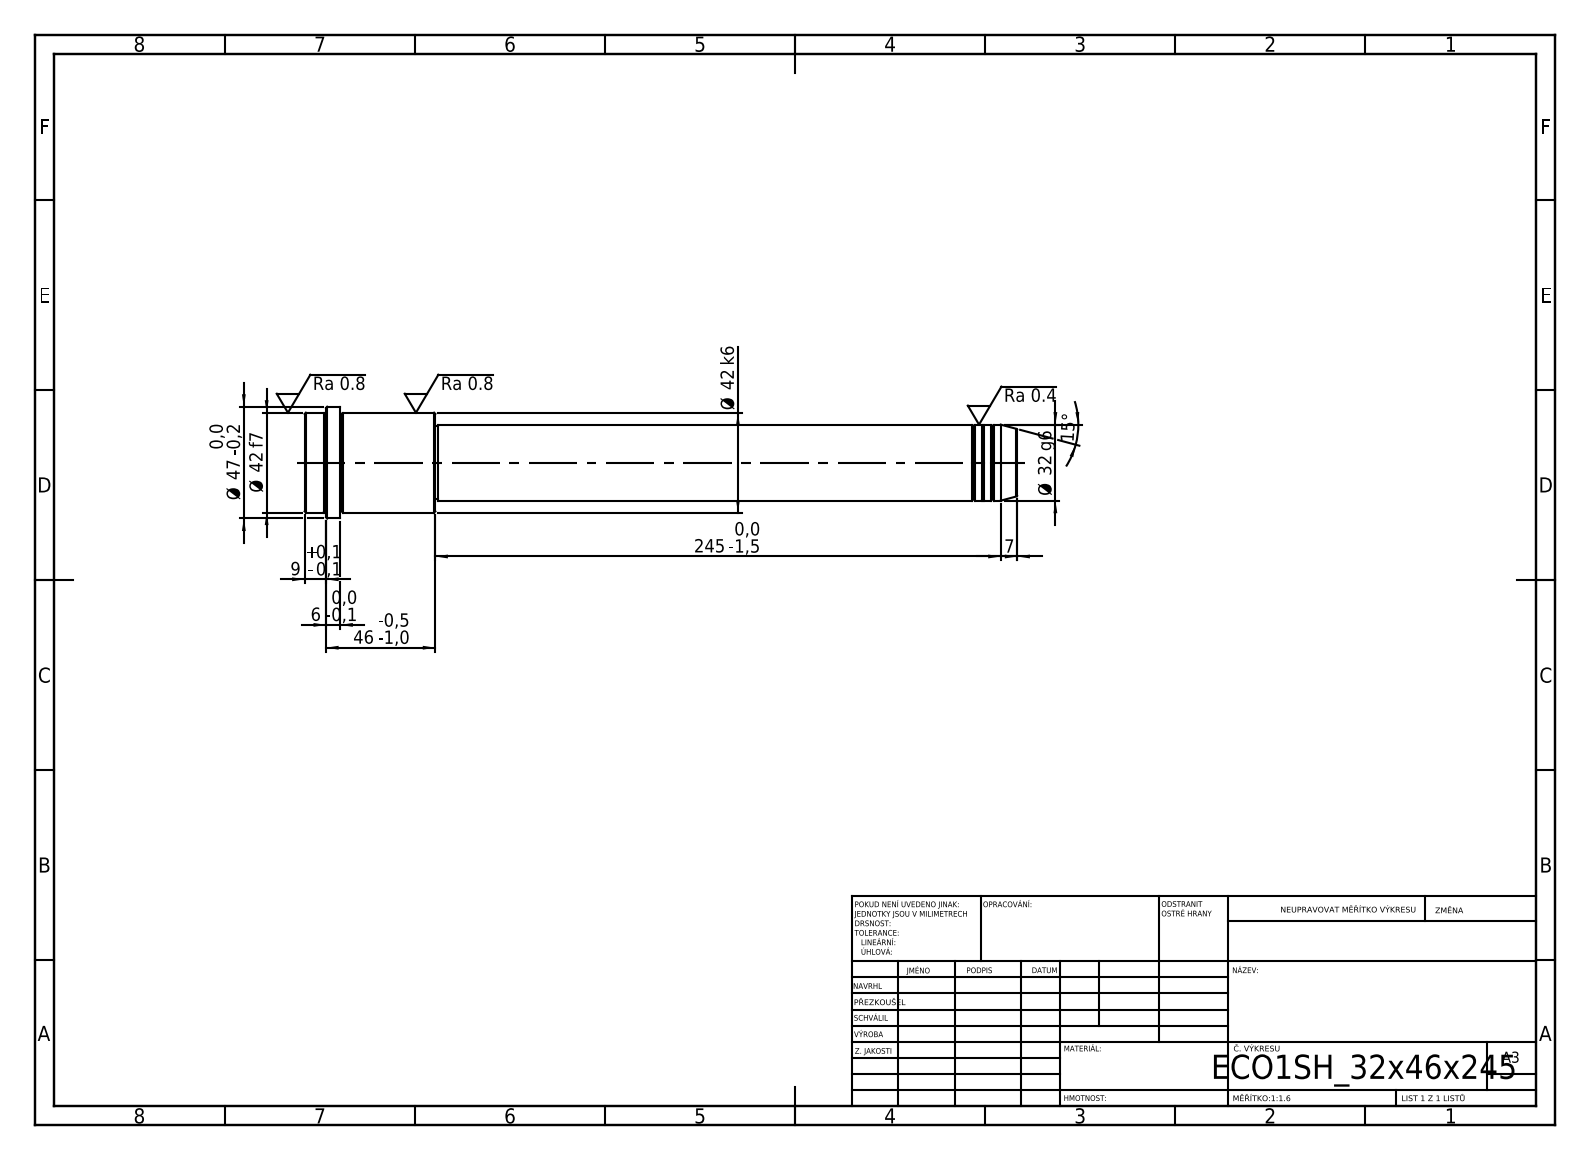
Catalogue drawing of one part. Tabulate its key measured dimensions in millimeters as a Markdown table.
| quantity | value |
| --- | --- |
| STEP written by | SolidWorks 2019 (CONFIG_CONTROL_DESIGN) |
| units | millimeters |
| bodies | 1 solid, 52 faces (6 planar, 16 cylindrical, 30 other) |
| overall size | 300 × 47 × 47 |
| volume | 274 380 mm³ |
| surface area | 35 527 mm² |
| round bosses / shafts (diameter × count) | 47 × 1, 42 × 1, 32 × 1, 31 × 1 |
| main face-to-face distances | 300, 245, 55, 285, 40, 15, 291, 46, 6, 9 |
